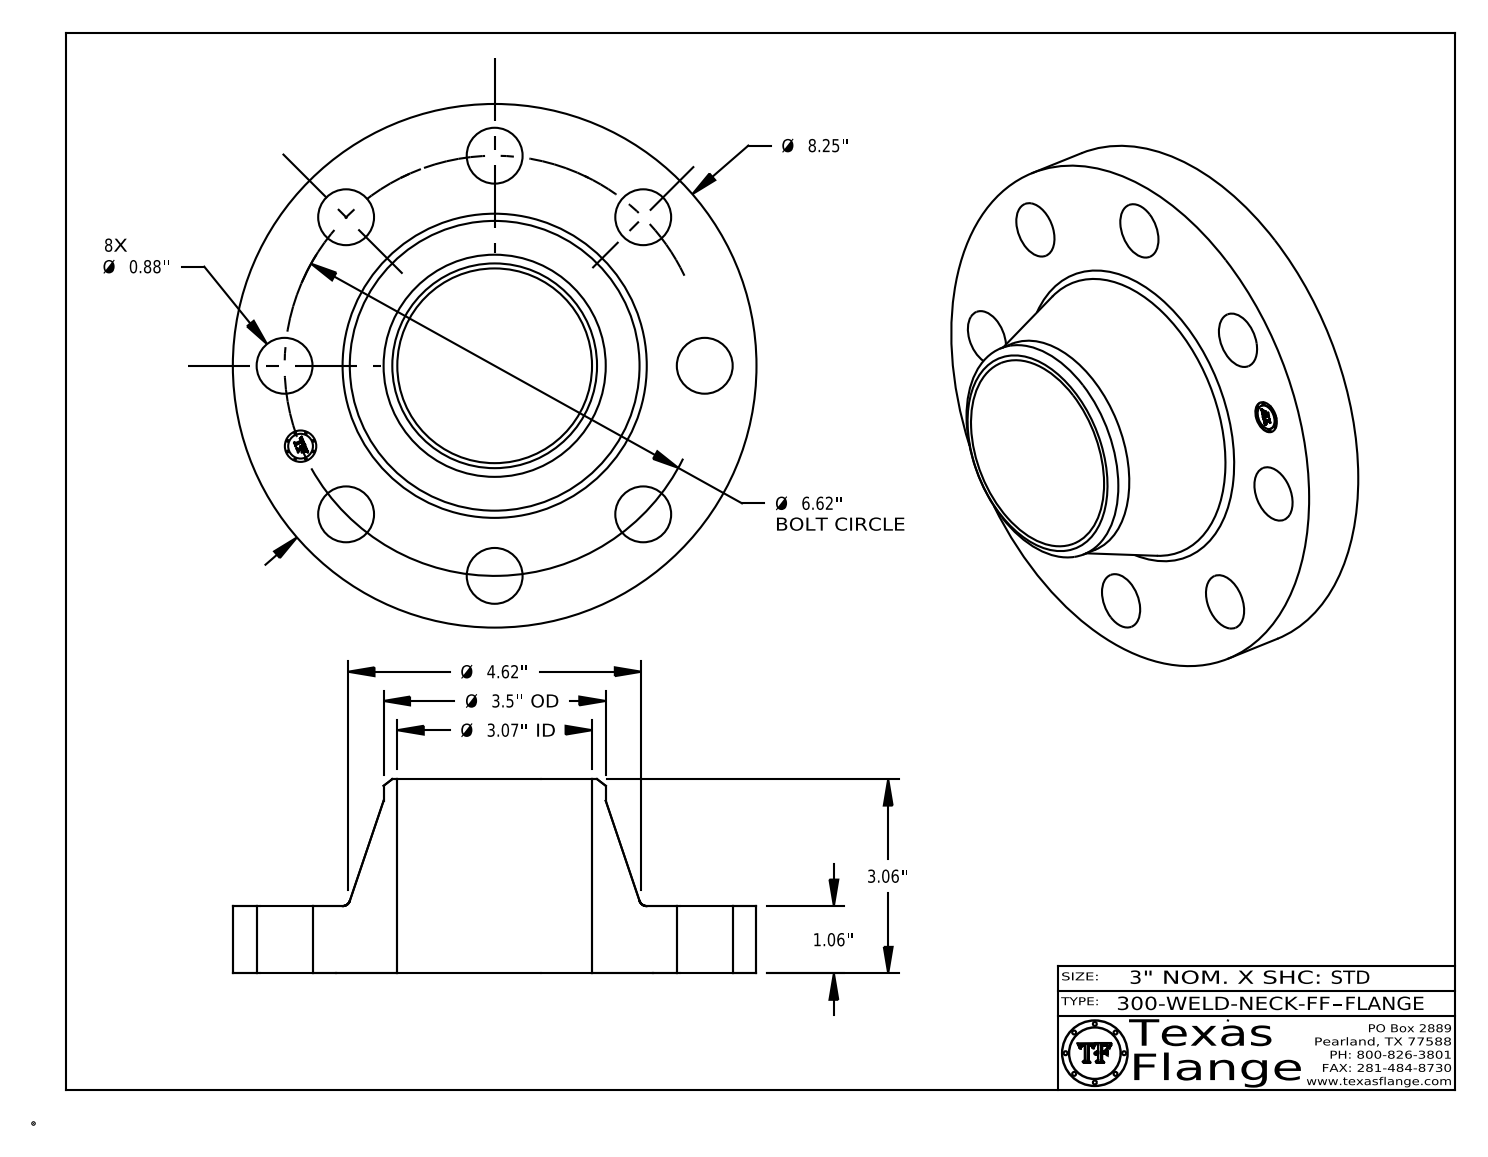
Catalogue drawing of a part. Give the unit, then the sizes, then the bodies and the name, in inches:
Units: inches
Overall size (bounding box): 8.25 × 8.25 × 3.06
Round holes (diameter × count): ⌀0.88 ×8, ⌀0.495 ×1, ⌀3.068 ×1
Round bosses / shafts (diameter × count): ⌀0.03 ×8, ⌀8.25 ×1, ⌀3.5 ×1, ⌀0.39 ×1
Main face-to-face distances: 1.06, 3.06, 2, 0.015, 1.045, 2.015, 0.148, 0.145, 0.027, 0.096
Hole centre spacings: 3.31, 2.533, 6.116, 4.681, 4.681, 1.291, 3.678, 6.493
Volume: 53.72 in³ · Surface area: 180.7 in²
Bodies: 1 solid, 417 faces (369 planar, 42 cylindrical, 6 other)
Part name (STEP PRODUCT): 300-WELD-NECK-FF
STEP written by: CATIA V5 STEP AP214 (AUTOMOTIVE_DESIGN)
